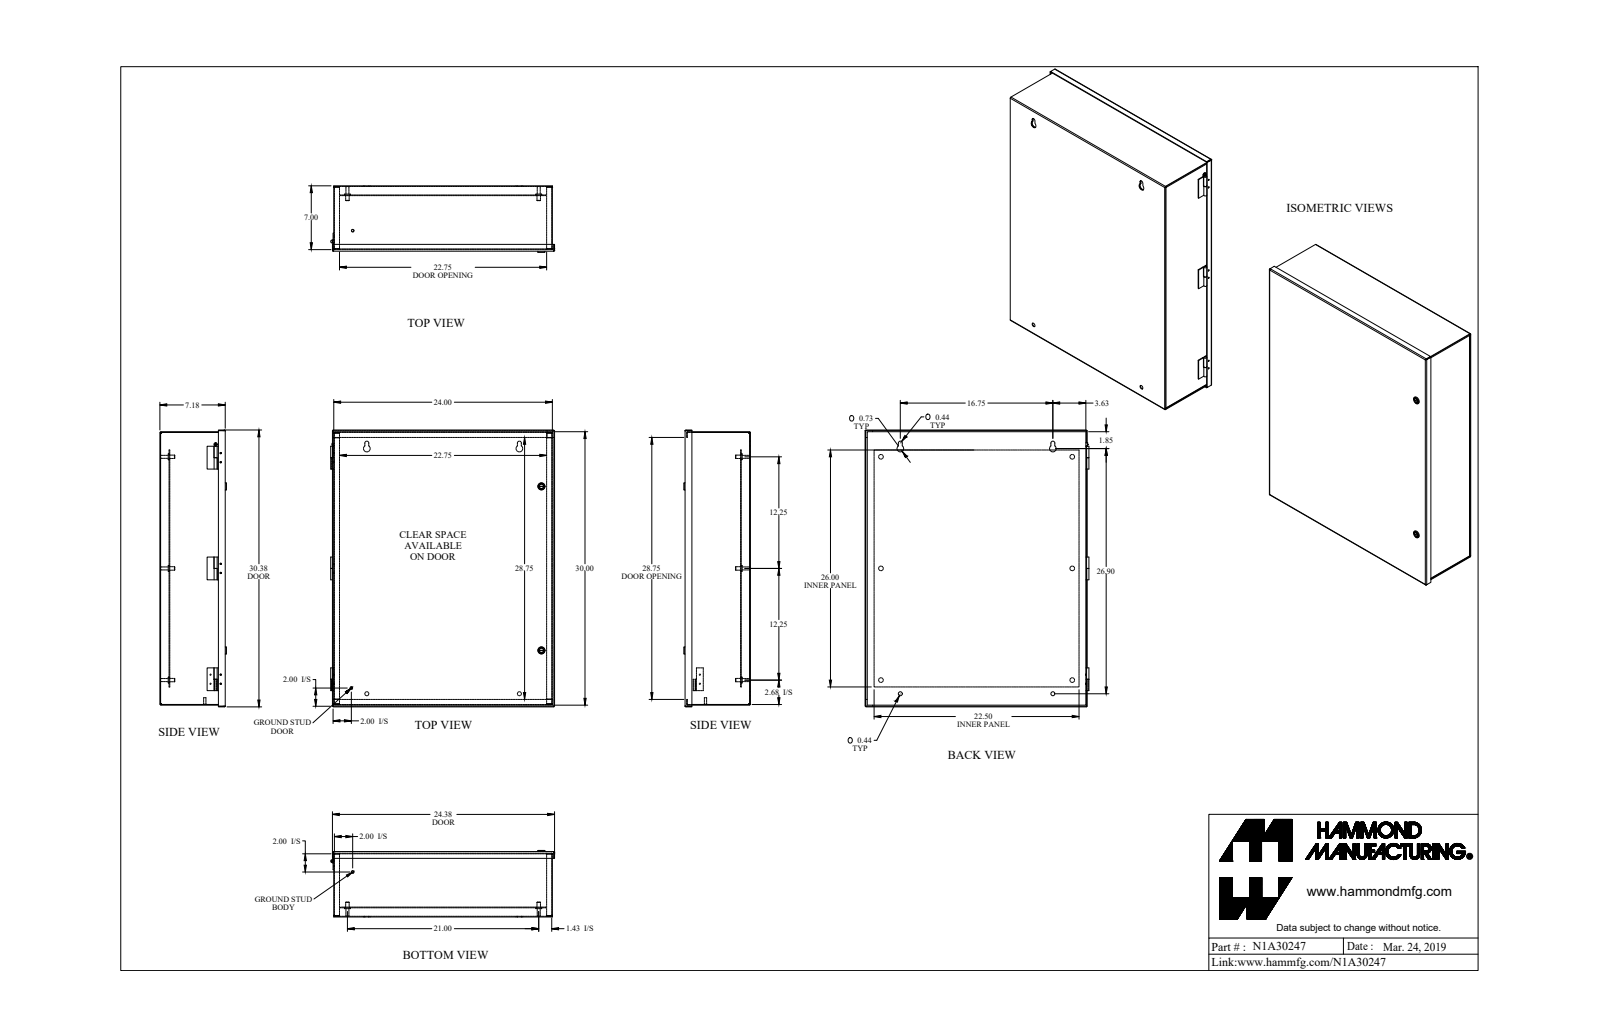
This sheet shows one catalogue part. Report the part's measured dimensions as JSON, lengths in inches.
{"part_name": "N1A30247", "step_written_by": "SolidWorks 2018 (AUTOMOTIVE_DESIGN)", "units": "inches", "bodies": {"solids": 34, "faces": 767, "planar": 434, "cylindrical": 269, "other": 64}, "overall_size": [30.384, 24.574, 7.299], "volume_in3": 217.5, "surface_area_in2": 6052, "round_holes": [[0.14, 12], [0.5, 6], [0.307, 4], [0.445, 4], [0.437, 2], [0.516, 2], [0.734, 2], [0.17, 1], [0.187, 1]], "round_bosses_or_shafts": [[0.128, 12], [0.375, 7], [0.65, 6], [0.33, 6], [1, 4], [0.788, 2], [0.535, 2], [0.496, 2]], "partial_cylinders_radius": [[0.036, 16], [0.108, 16], [0.06, 2], [0.125, 2], [0.153, 2], [0.219, 2], [0.315, 2], [0.03, 1]], "face_to_face_distances": [0.072, 7.105, 1.009, 6.096, 7.033, 7.177, 0.937, 1.081, 6.024, 6.168], "hole_center_spacings": [1, 1.119, 24.312, 12.156, 12.157, 12.207, 12.209, 12.25]}
